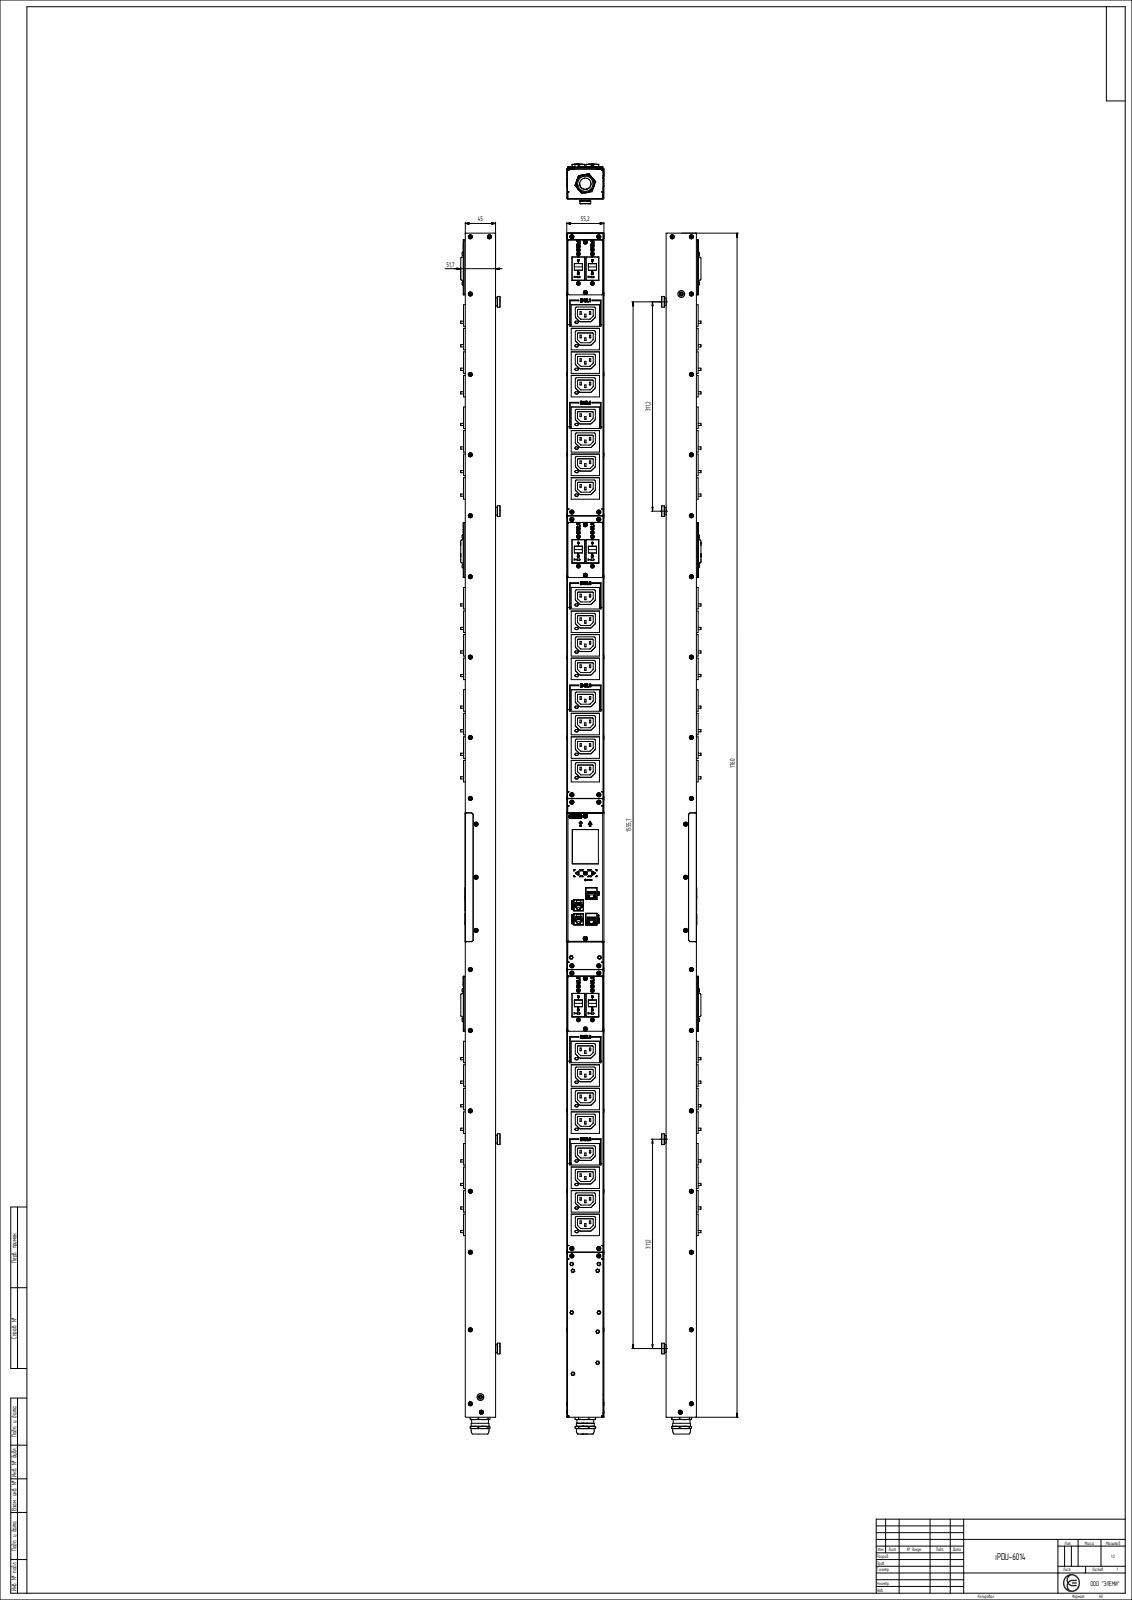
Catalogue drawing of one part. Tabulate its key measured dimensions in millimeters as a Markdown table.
| quantity | value |
| --- | --- |
| part name | iPDU-6014 |
| STEP written by | C3D Toolkit (AUTOMOTIVE_DESIGN) |
| units | millimeters |
| bodies | 163 solids, 3248 faces (2130 planar, 527 cylindrical, 591 other) |
| overall size | 1785 × 55.2 × 51.72 |
| volume | 4 494 000 mm³ |
| surface area | 400 524 mm² |
| round holes (diameter × count) | 4 × 10, 10 × 2, 2.5 × 1, 14 × 1 |
| round bosses / shafts (diameter × count) | 26.5 × 1, 0.82 × 1, 0.64 × 1 |
| partial cylindrical surfaces (radius × count) | 2 × 168, 1 × 144, 1.45 × 96, 0.25 × 52, 0.76 × 20, 0.1 × 4, 0.4 × 4, 0.55 × 4 |
| main face-to-face distances | 55.2, 45, 47.6, 2.6, 0.4, 3, 48, 51.72, 6.72, 4.12 |
| hole center spacings | 25, 87.52, 95.94, 397.97, 406.47, 783.2, 954.48, 1331.28 |
